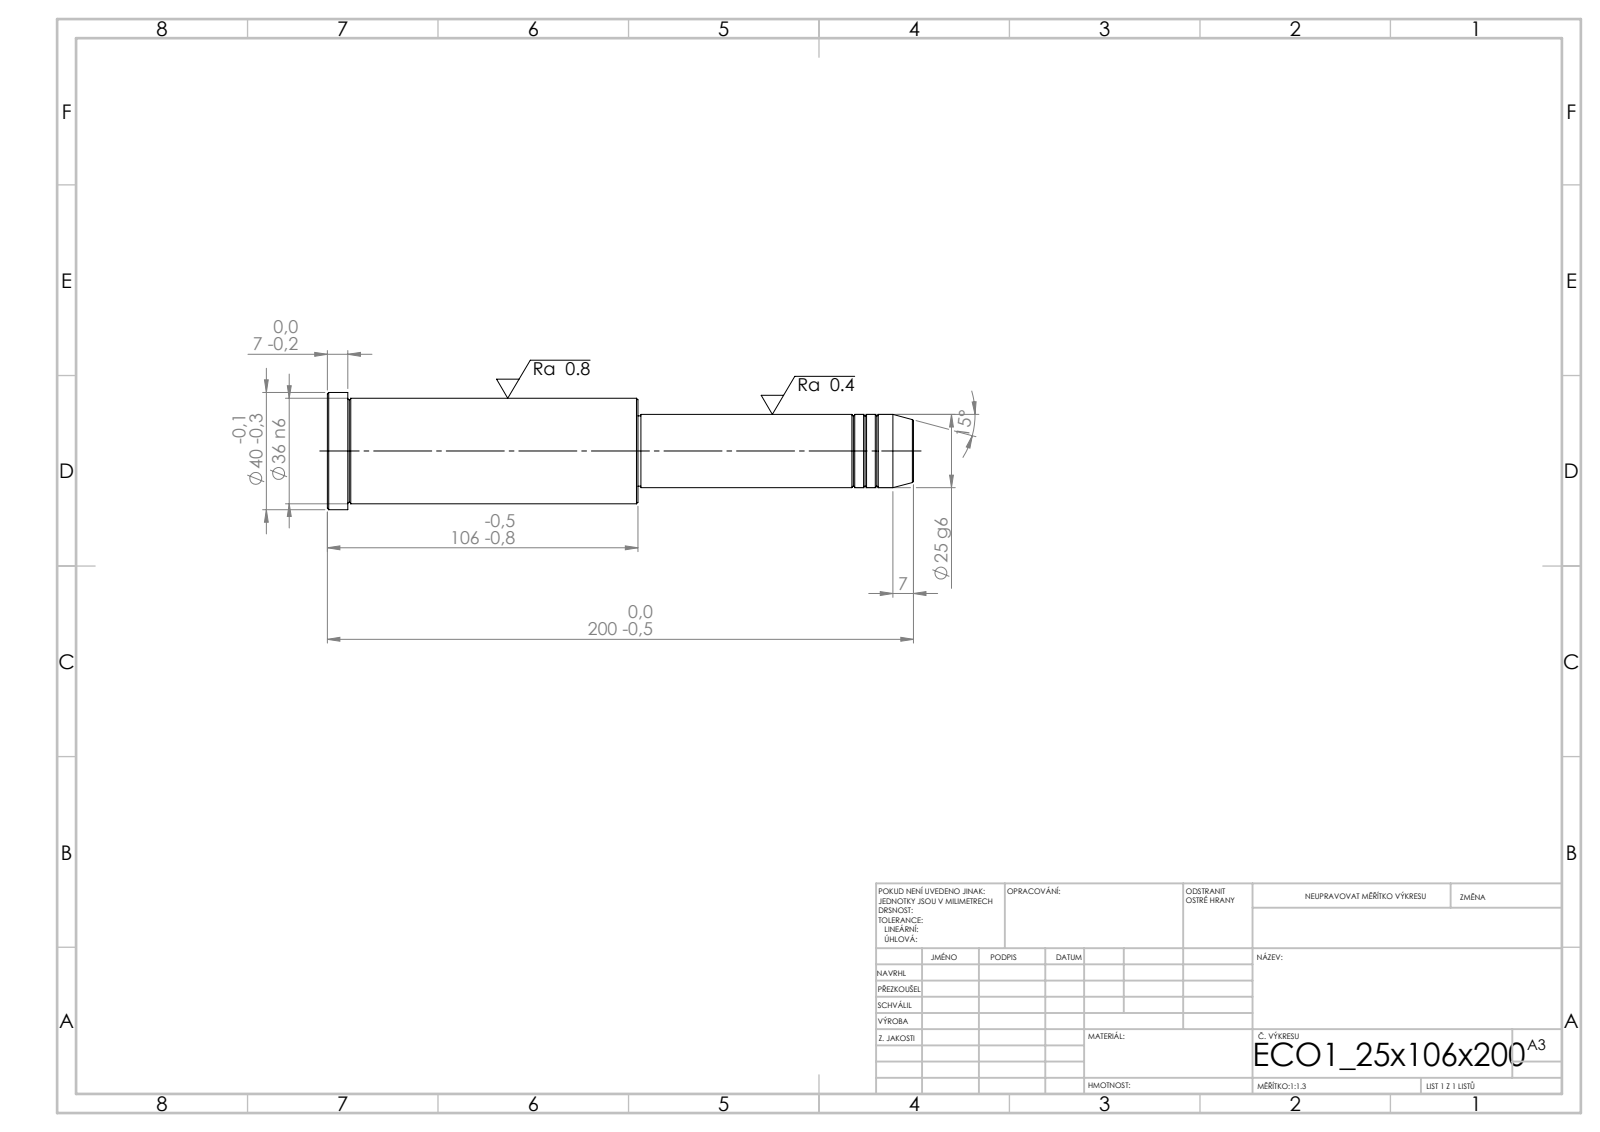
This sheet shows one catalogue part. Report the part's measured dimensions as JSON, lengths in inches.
{"step_written_by": "SolidWorks 2019 (CONFIG_CONTROL_DESIGN)", "units": "inches", "bodies": {"solids": 1, "faces": 43, "planar": 5, "cylindrical": 14, "other": 24}, "overall_size": [7.874, 1.575, 1.575], "volume_in3": 9.46, "surface_area_in2": 34.09, "round_bosses_or_shafts": [[1.575, 1], [1.417, 1], [0.984, 1], [0.945, 1]], "face_to_face_distances": [4.173, 3.701, 7.874, 7.598, 3.898, 0.276, 3.661, 0.039, 3.937, 4.213]}
